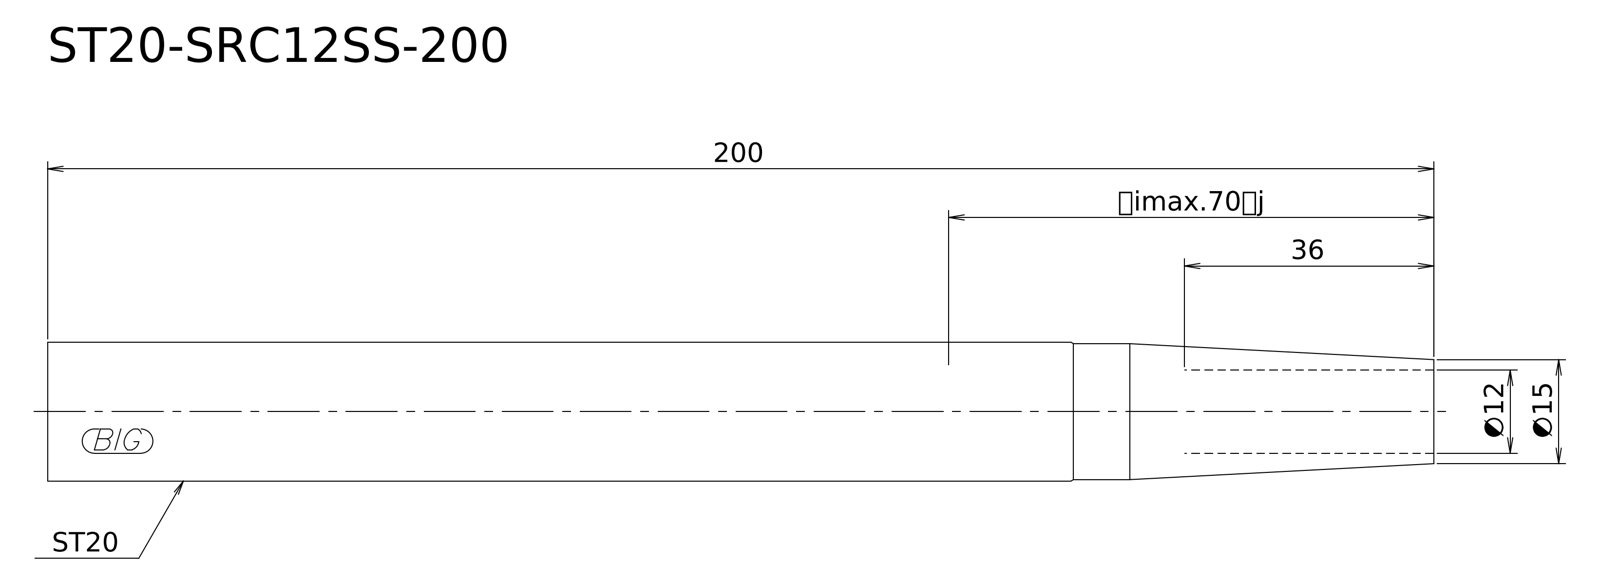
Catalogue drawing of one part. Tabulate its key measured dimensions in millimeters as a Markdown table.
| quantity | value |
| --- | --- |
| STEP written by | Kubotek KeyCreator V8.5.1 (14335) (CONFIG_CONTROL_DESIGN) |
| units | millimeters |
| bodies | 1 solid, 6 faces (2 planar, 2 cylindrical, 2 other) |
| overall size | 200 × 20 × 20 |
| volume | 59 318 mm³ |
| surface area | 12 681 mm² |
| round bosses / shafts (diameter × count) | 20 × 1, 19.6 × 1 |
| main face-to-face distances | 200 |
